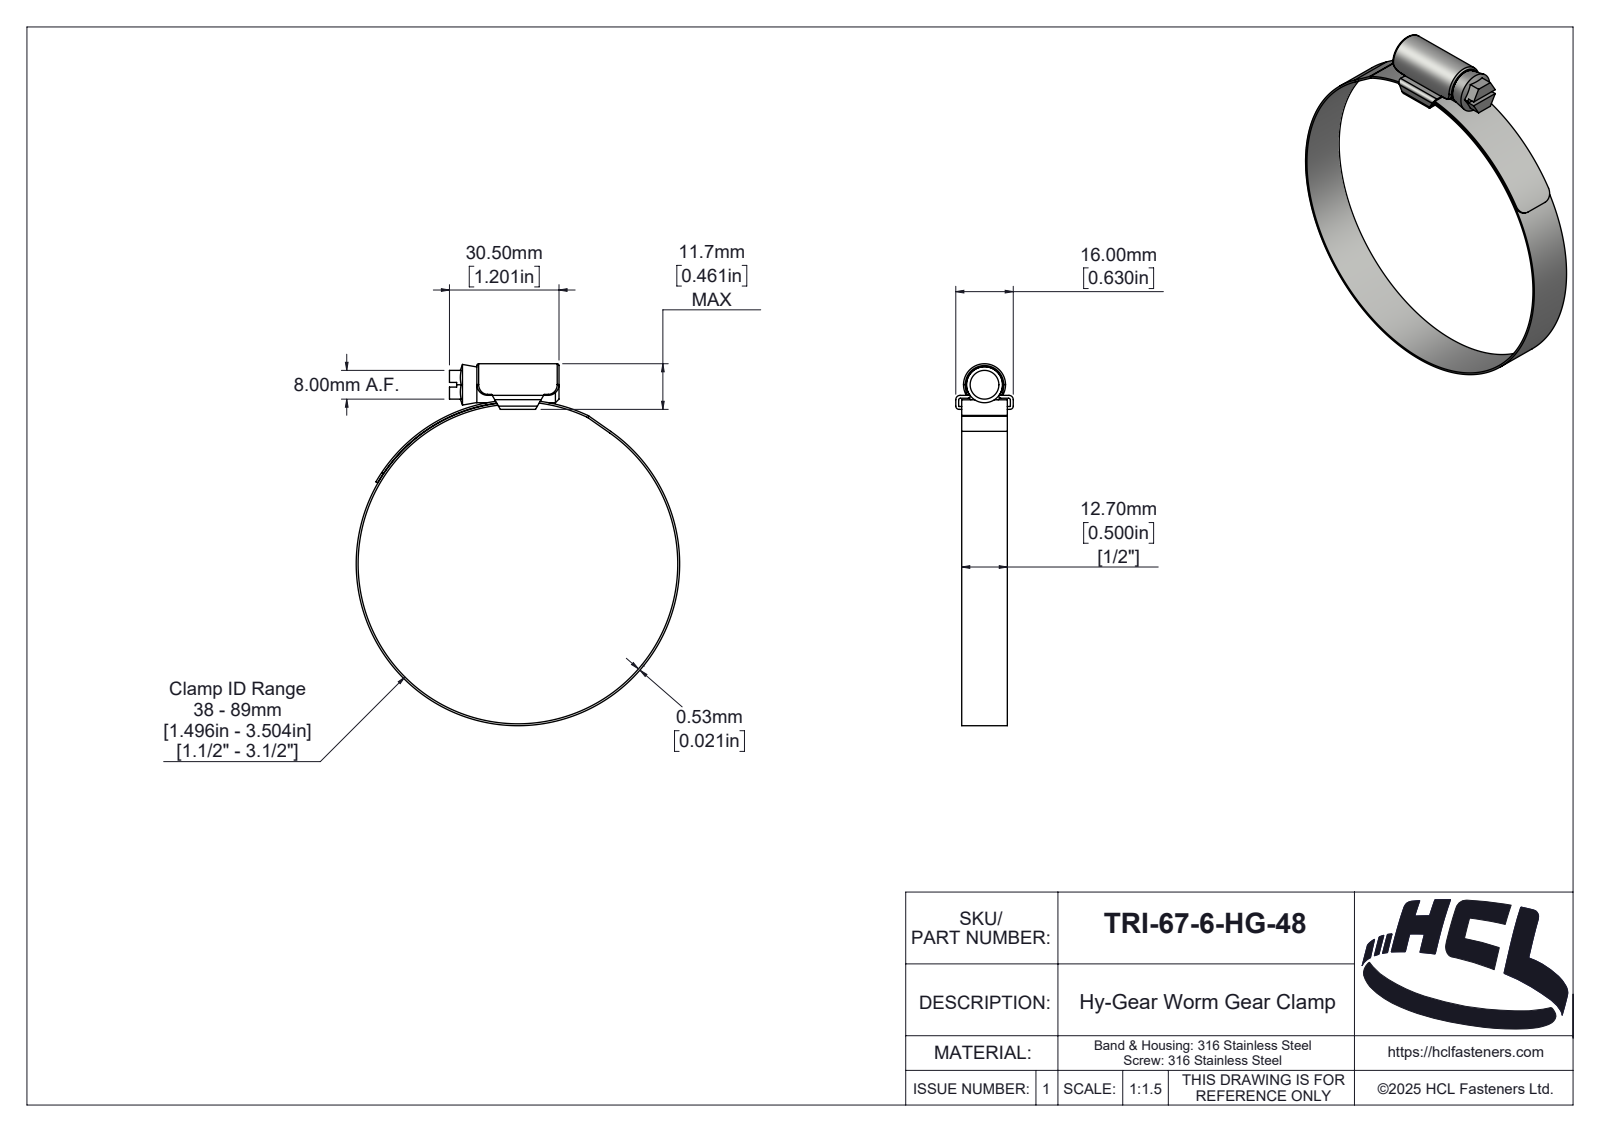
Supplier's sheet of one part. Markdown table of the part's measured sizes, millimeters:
| quantity | value |
| --- | --- |
| part name | TRI-57-0-HG-48 |
| STEP written by | SolidWorks 2025 (AUTOMOTIVE_DESIGN) |
| units | millimeters |
| bodies | 3 solids, 189 faces (39 planar, 89 cylindrical, 61 other) |
| overall size | 100.73 × 90.06 × 16 |
| volume | 5 206 mm³ |
| surface area | 11 613 mm² |
| round holes (diameter × count) | 89 × 1 |
| round bosses / shafts (diameter × count) | 90.06 × 1, 10 × 1 |
| partial cylindrical surfaces (radius × count) | 0.5 × 6, 3 × 4, 0.1 × 2, 0.9 × 2, 1.2 × 2, 0.46 × 1, 1.89 × 1, 2 × 1 |
| main face-to-face distances | 0.8, 12.7, 3.1, 0.53, 2.3, 3.9, 30.5, 1.65, 14.35, 15.2 |
